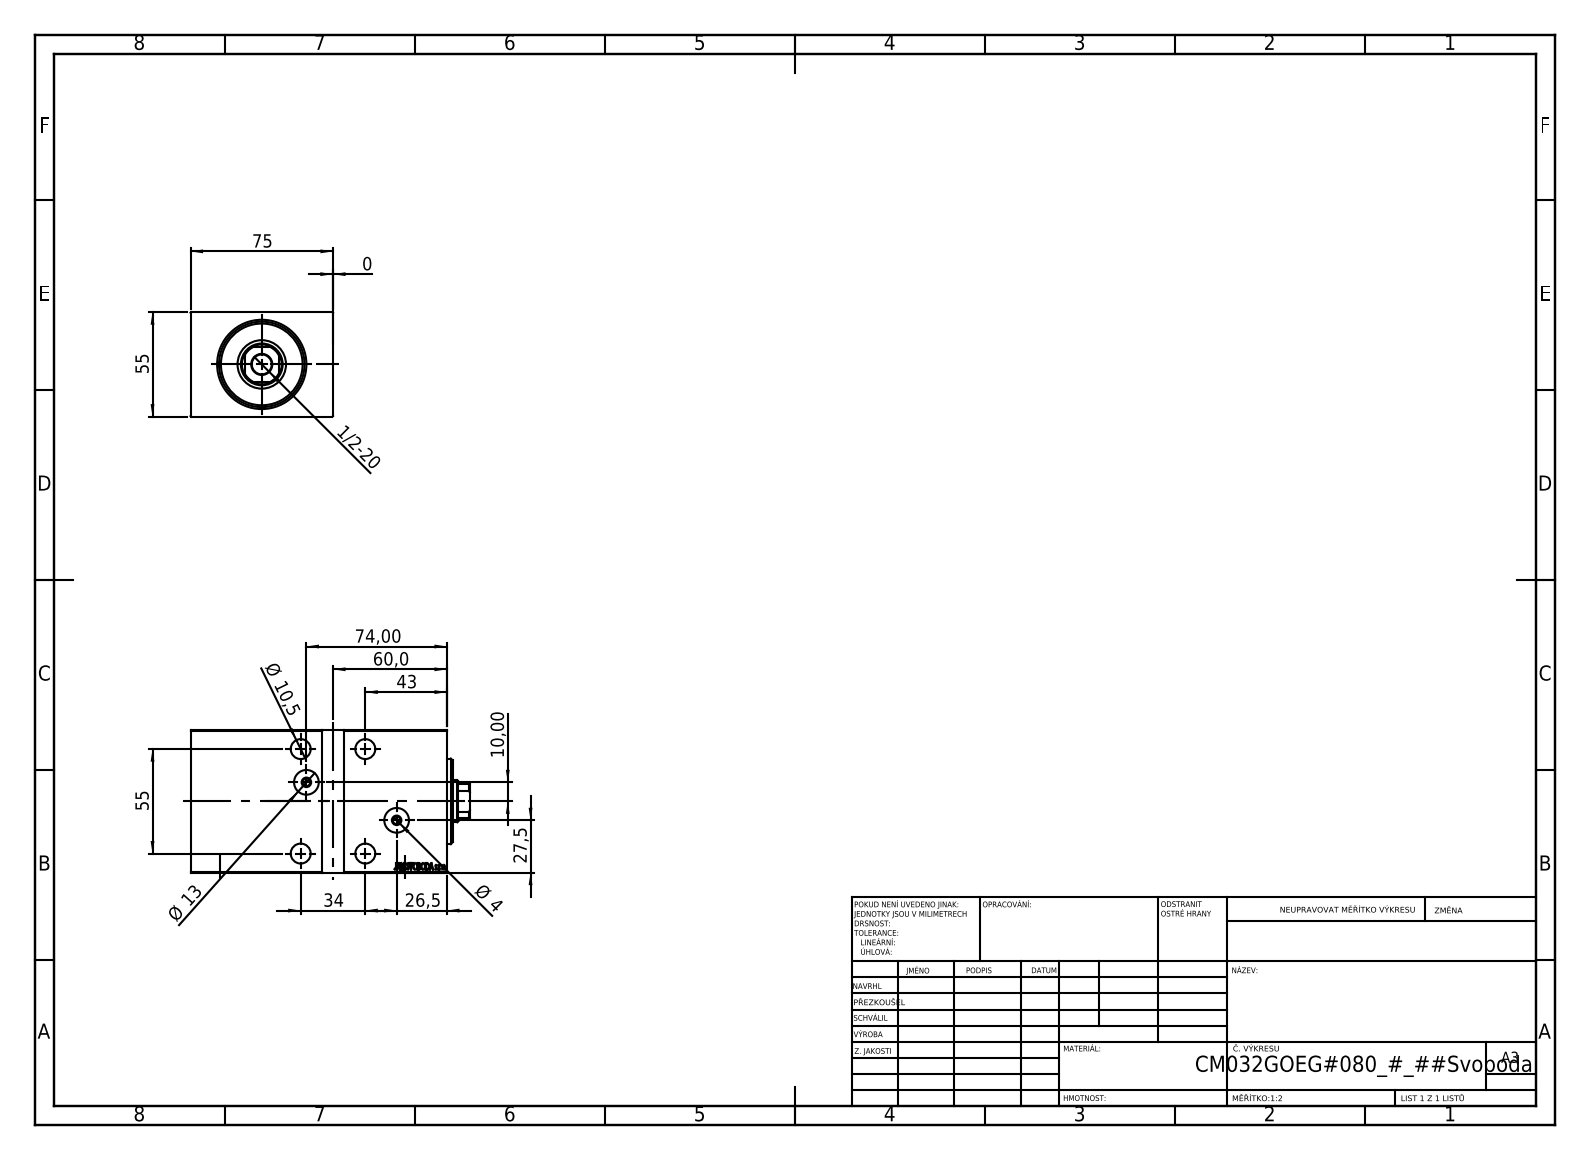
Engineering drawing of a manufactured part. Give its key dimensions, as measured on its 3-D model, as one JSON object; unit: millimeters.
{"part_name": "V450CM_G_Body; V450CM_VC_G; Zatka_OIL_PORT; V450CM_G_VCP", "step_written_by": "SolidWorks 2019 (CONFIG_CONTROL_DESIGN)", "units": "millimeters", "bodies": {"solids": 5, "faces": 896, "planar": 442, "cylindrical": 56, "other": 398}, "overall_size": [147, 75, 55], "volume_mm3": 498699, "surface_area_mm2": 83816, "round_holes": [[10.5, 5], [16.5, 4], [4, 2], [13, 2], [22, 1], [25.5, 1], [32, 1], [34, 1], [45, 1]], "round_bosses_or_shafts": [[18, 2], [5, 2], [27, 1]], "partial_cylinders_radius": [[10.5, 1]], "face_to_face_distances": [55, 75, 135, 5, 3, 130, 125, 10, 120, 138], "hole_center_spacings": [34, 55, 64.66, 17.76, 24.05, 35.6, 37.62, 40.97]}
